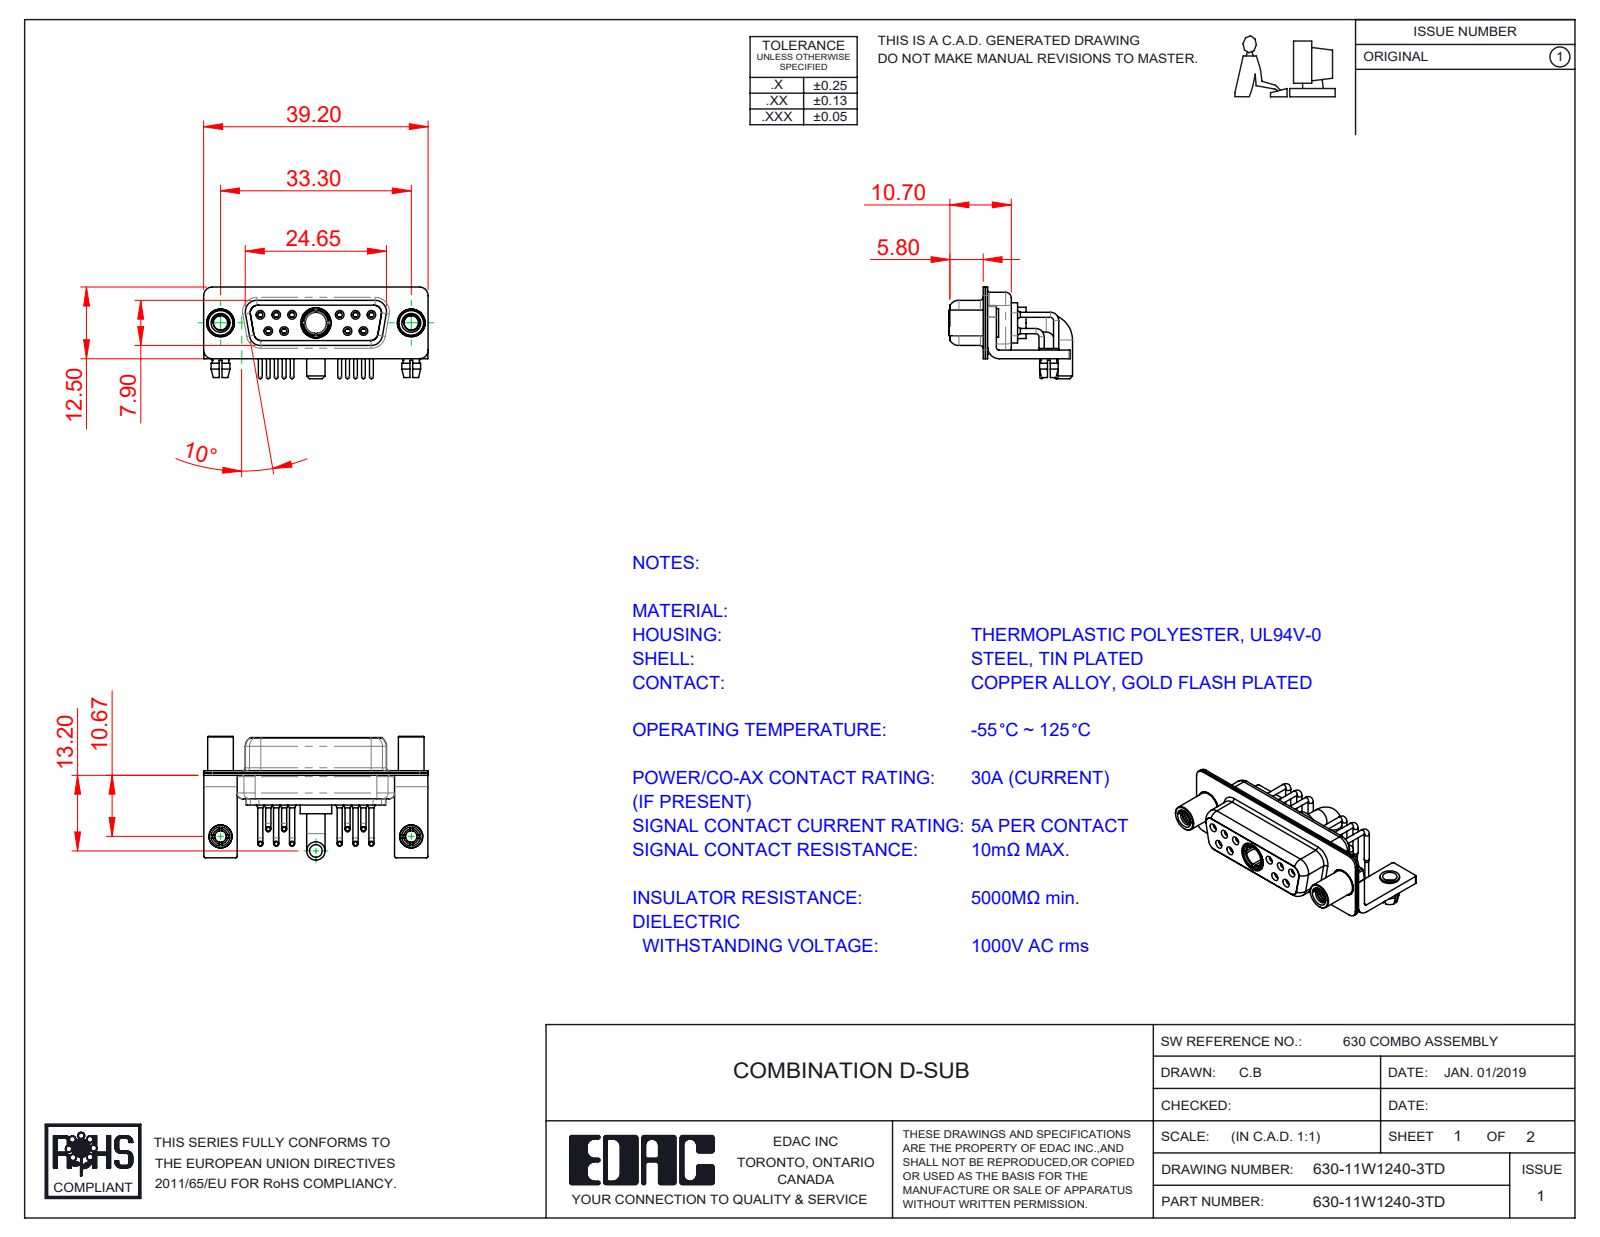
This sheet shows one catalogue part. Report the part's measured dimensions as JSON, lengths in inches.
{"part_name": "Power Socket_30A RA; 630Combo Shell Front_15 Contacts; 630Combo Threaded Standoff_D; 630Combo Stabilizer Bracket (+6 more)", "step_written_by": "SolidWorks 2020 (CONFIG_CONTROL_DESIGN)", "units": "inches", "bodies": {"solids": 21, "faces": 1077, "planar": 316, "cylindrical": 496, "other": 265}, "overall_size": [1.543, 0.85, 0.63], "volume_in3": 0.189, "surface_area_in2": 11.51, "round_holes": [[0.079, 12], [0.035, 10], [0.043, 10], [0.059, 10], [0.067, 6], [0.063, 4], [0.098, 4], [0.191, 3], [0.126, 2], [0.157, 2], [0.159, 2], [0.146, 1]], "round_bosses_or_shafts": [[0.035, 10], [0.026, 10], [0.063, 6], [0.197, 2], [0.195, 2], [0.189, 2], [0.177, 2], [0.157, 2]], "partial_cylinders_radius": [[0.01, 16], [0.059, 16], [0.079, 13], [0.053, 12], [0.063, 8], [0.02, 5], [0.024, 4], [0.026, 4]], "face_to_face_distances": [0.016, 0.031, 0.018, 0.055, 0.333, 0.059, 0.071, 0.35, 0.244, 0.091], "hole_center_spacings": [0.124, 0.109, 0.545, 0.436, 0.654, 0.198, 0.198, 0.218]}
